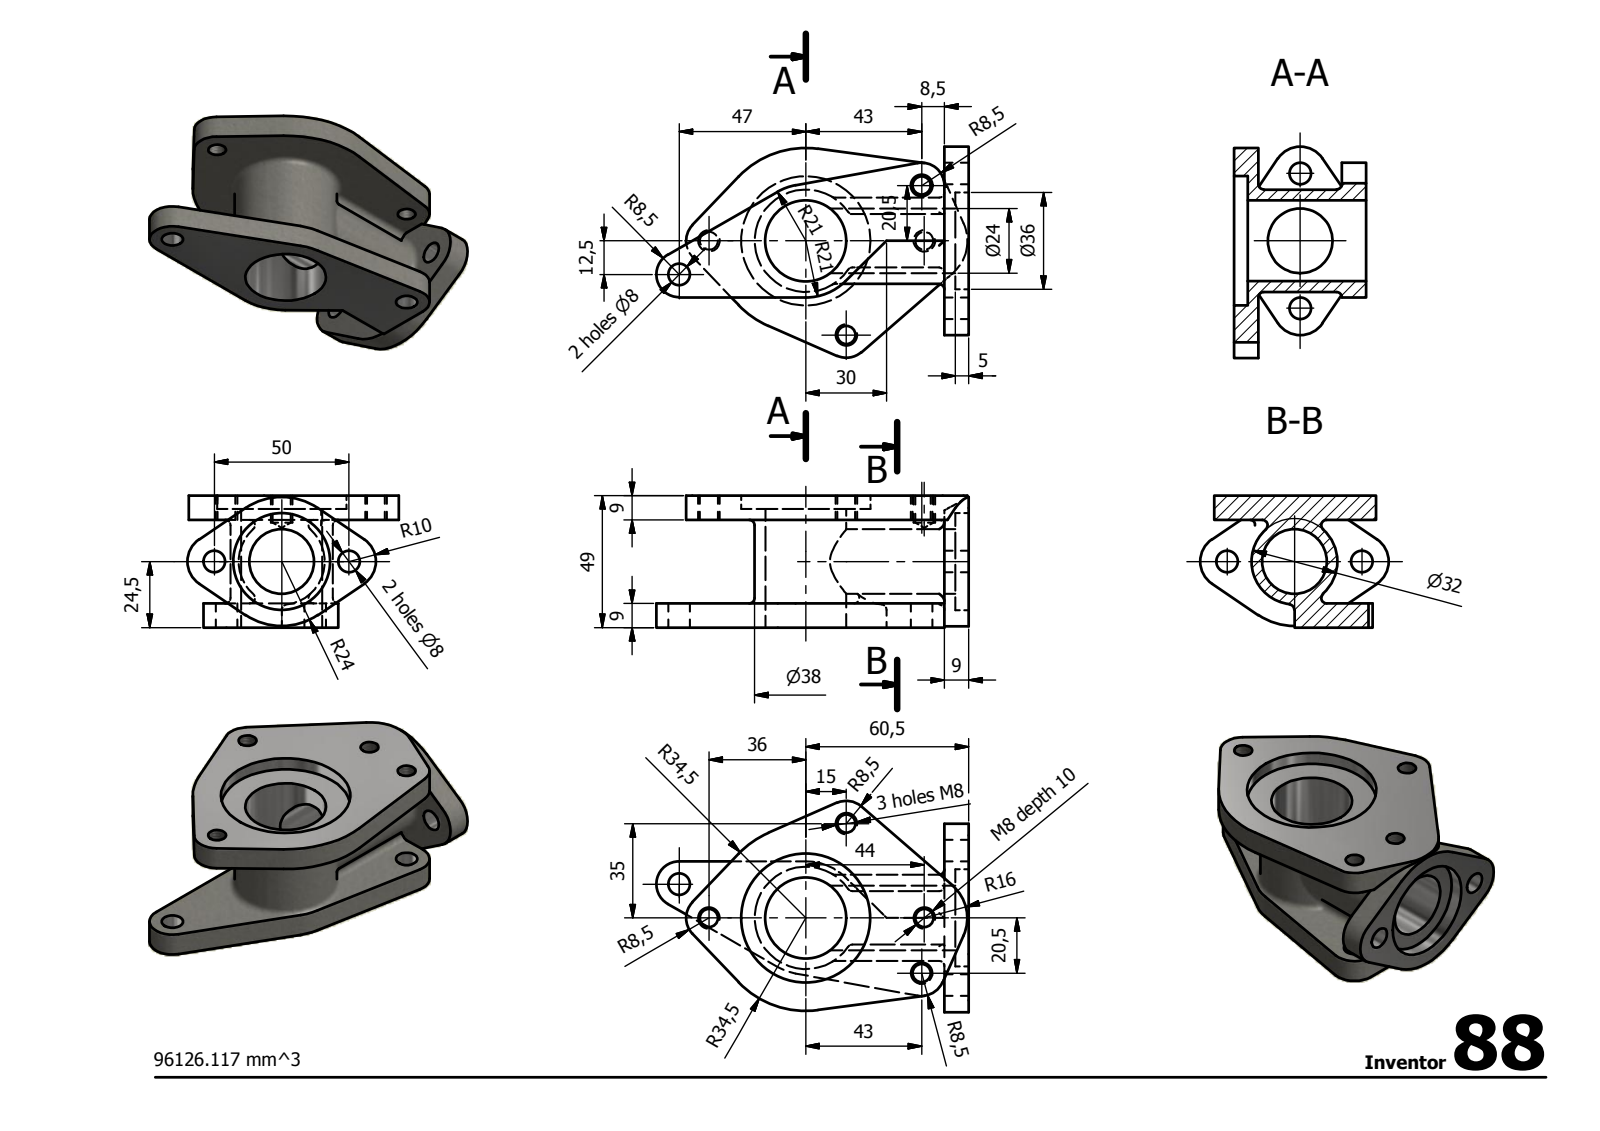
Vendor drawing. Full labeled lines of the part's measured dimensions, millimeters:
STEP written by: Autodesk Inventor 2014 (AUTOMOTIVE_DESIGN)
Units: millimetres
Bodies: 1 solid, 74 faces (27 planar, 35 cylindrical, 12 other)
Overall size (bounding box): 116 × 78.5 × 49
Volume: 96 125 mm³ · Surface area: 36 399 mm²
Round holes (diameter × count): ⌀6.65 ×4, ⌀8 ×4, ⌀24 ×1, ⌀30 ×1, ⌀36 ×1, ⌀48 ×1
Round bosses / shafts (diameter × count): ⌀38 ×1
Partial cylindrical surfaces — rounded edges, fillets, slot ends (radius × count): R2 ×6, R8.5 ×4, R10 ×2, R16 ×2, R21 ×1, R24 ×1, R34.5 ×1
Main face-to-face distances: 9, 40, 49, 4, 5, 31, 44, 35, 47.99, 47.98
Hole centre spacings: 25, 16.65, 20.52, 36, 38.08, 44, 45.45, 47.64
